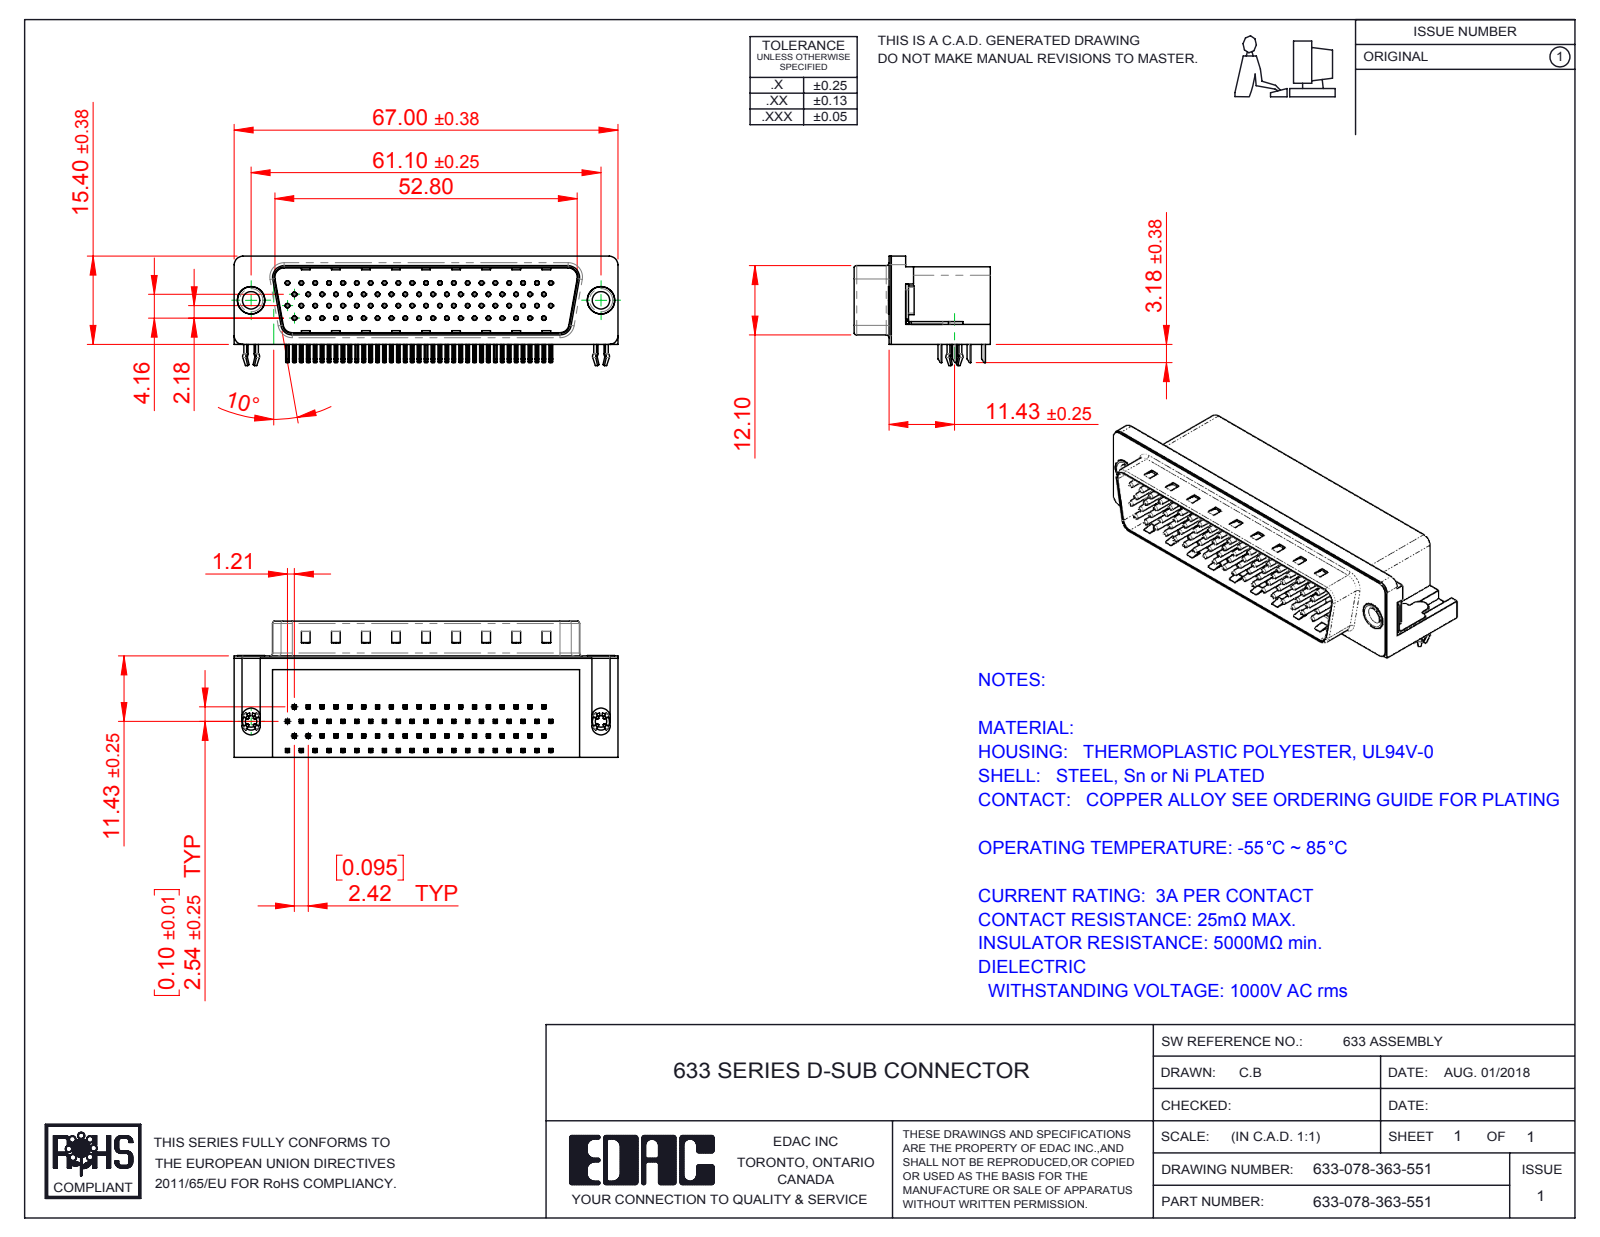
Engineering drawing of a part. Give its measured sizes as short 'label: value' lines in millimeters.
name: 633 Contact Middle_78 Contact; 633 Contact Bottom_78 Contact; 633 Housing_78 Contact; 633 Shell_78 Contact (+5 more)
written by: SolidWorks 2016 (CONFIG_CONTROL_DESIGN)
unit: mm
bodies: 84 solids, 6356 faces (4023 planar, 1766 cylindrical, 567 other)
size: 67 × 23.8 × 19.1
volume: 14 611 mm³; area: 16 410 mm²
holes: 78× ⌀0.35, 78× ⌀0.8, 2× ⌀2, 2× ⌀3.05, 2× ⌀4, 2× ⌀4.8, 2× ⌀5
bosses: 78× ⌀0.75, 2× ⌀4.9, 2× ⌀4.75, 2× ⌀3.85, 2× ⌀3
rounds: 324× R0.25, 156× R0.12, 16× R1, 9× R0.5, 8× R1.6, 6× R1.5, 4× R0.45, 4× R0.9
face distances: 0.4, 13.2, 17.3, 11.7, 13.35, 2.05, 13.75, 1.65, 1.85, 11.9
hole spacings: 2.42, 4.84, 7.26, 9.68, 6.26, 7.13, 12.1, 8.62
